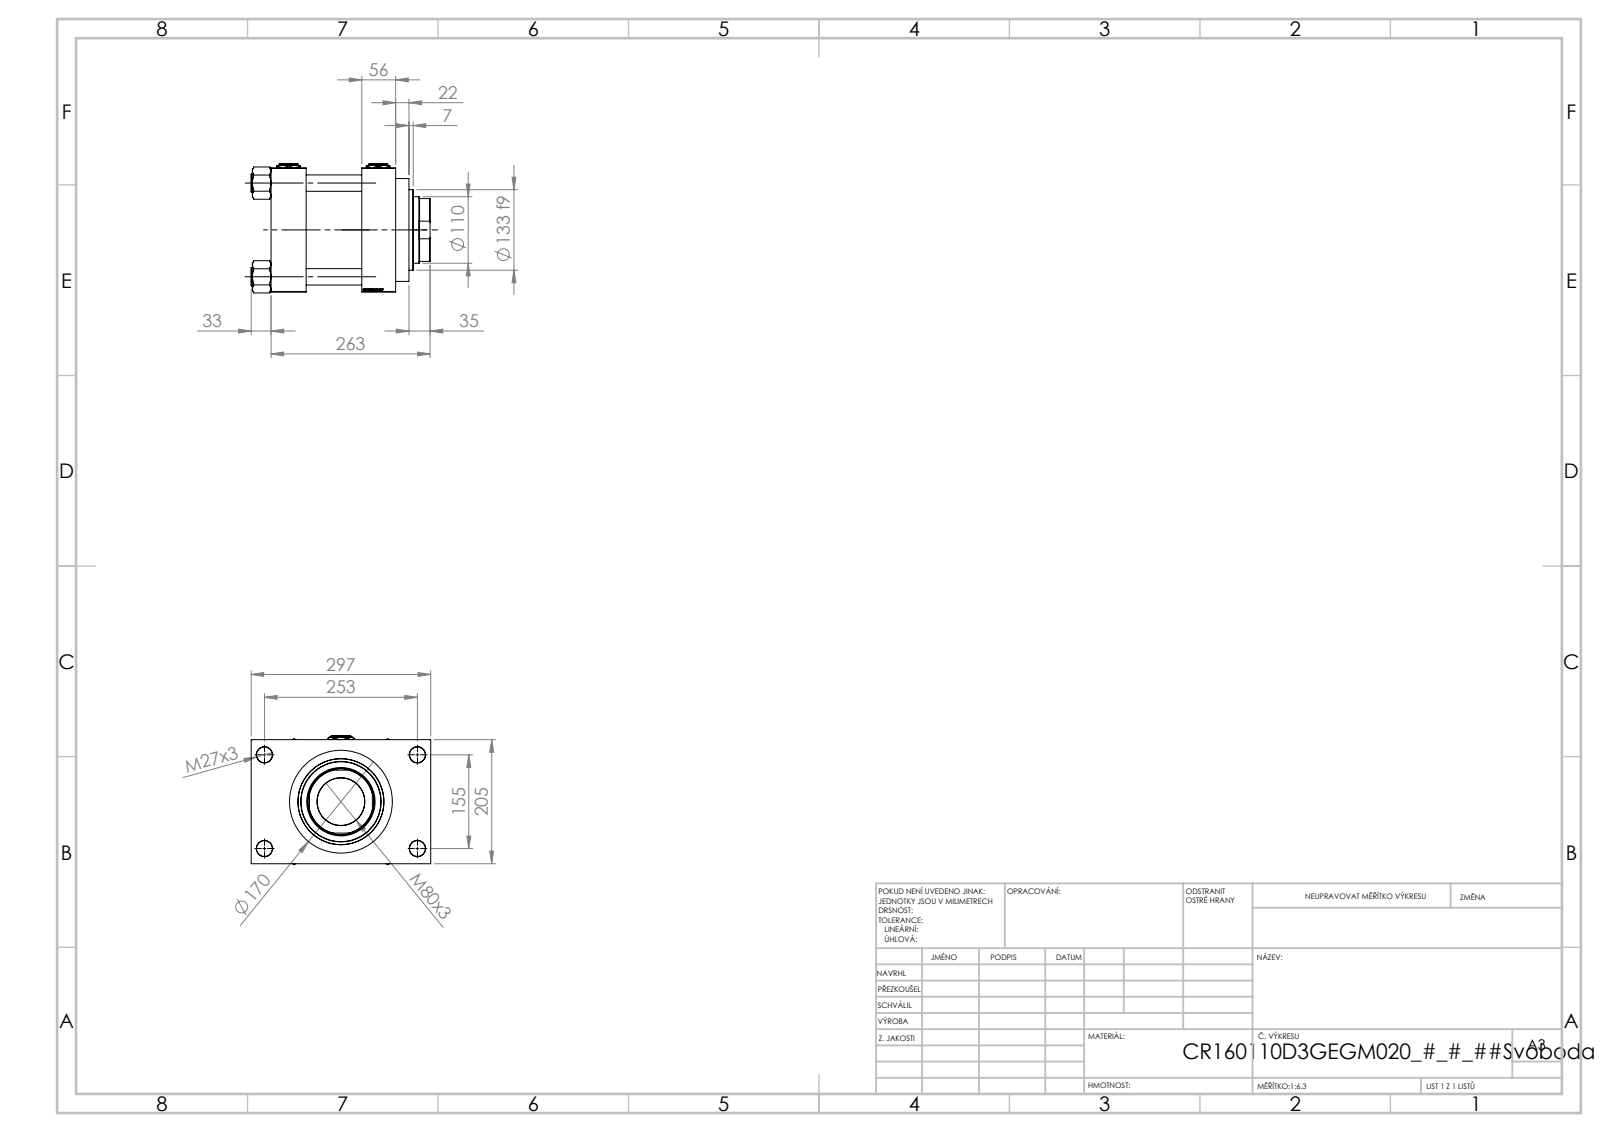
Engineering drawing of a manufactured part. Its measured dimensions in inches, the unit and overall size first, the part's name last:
Units: inches
Overall size (bounding box): 11.693 × 11.654 × 8.408
Round holes (diameter × count): ⌀1.024 ×4, ⌀1.063 ×4, ⌀0.276 ×2, ⌀1.309 ×2, ⌀1.772 ×2, ⌀3.091 ×1, ⌀4.331 ×1, ⌀4.449 ×1, ⌀4.724 ×1, ⌀5.591 ×1, ⌀6.299 ×1
Round bosses / shafts (diameter × count): ⌀1.181 ×4, ⌀6.693 ×1, ⌀6.535 ×1, ⌀5.236 ×1
Partial cylindrical surfaces — rounded edges, fillets, slot ends (radius × count): R2.126 ×1
Main face-to-face distances: 2.283, 5.906, 3.622, 8.071, 5.827, 2.205, 8.11, 1.811, 9.882, 2.835
Hole centre spacings: 1.931, 4.312, 5.841, 6.098, 6.399, 8.03, 10.084, 6.102
Volume: 496.4 in³ · Surface area: 1 219 in²
Bodies: 13 solids, 1253 faces (593 planar, 100 cylindrical, 560 other)
Part name (STEP PRODUCT): V215_VC_A; V215CR_D_Body; NUT_M5_D; V215CR_VCP_D (+2 more)
STEP written by: SolidWorks 2019 (CONFIG_CONTROL_DESIGN)
